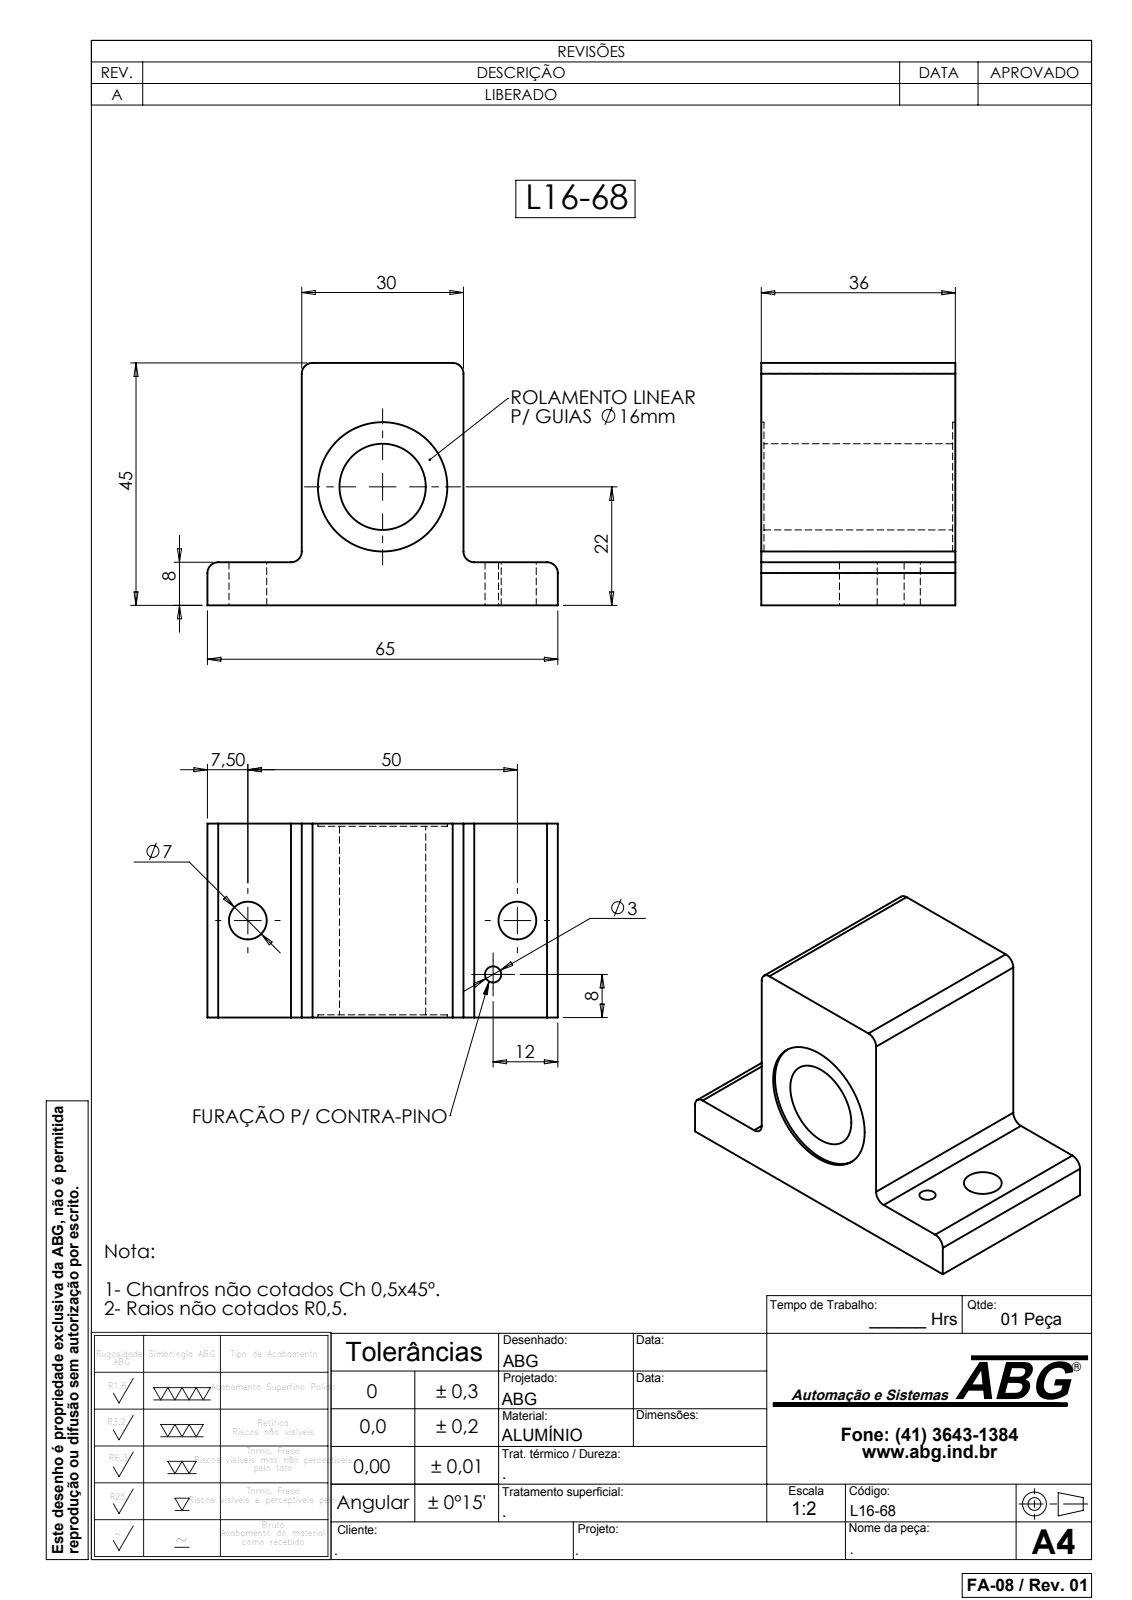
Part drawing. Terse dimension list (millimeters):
name: L16-68
written by: SolidWorks 2007 (CONFIG_CONTROL_DESIGN)
unit: mm
bodies: 1 solid, 30 faces (12 planar, 18 cylindrical, 0 other)
size: 65 × 45 × 36
volume: 50 456 mm³; area: 12 683 mm²
holes: 2× ⌀7, 1× ⌀3, 1× ⌀16, 1× ⌀24
rounds: 6× R2
face distances: 30, 36, 45, 8, 37, 0.5, 35.5, 17.5, 47.5, 35
hole spacings: 10.97, 46.59, 50
